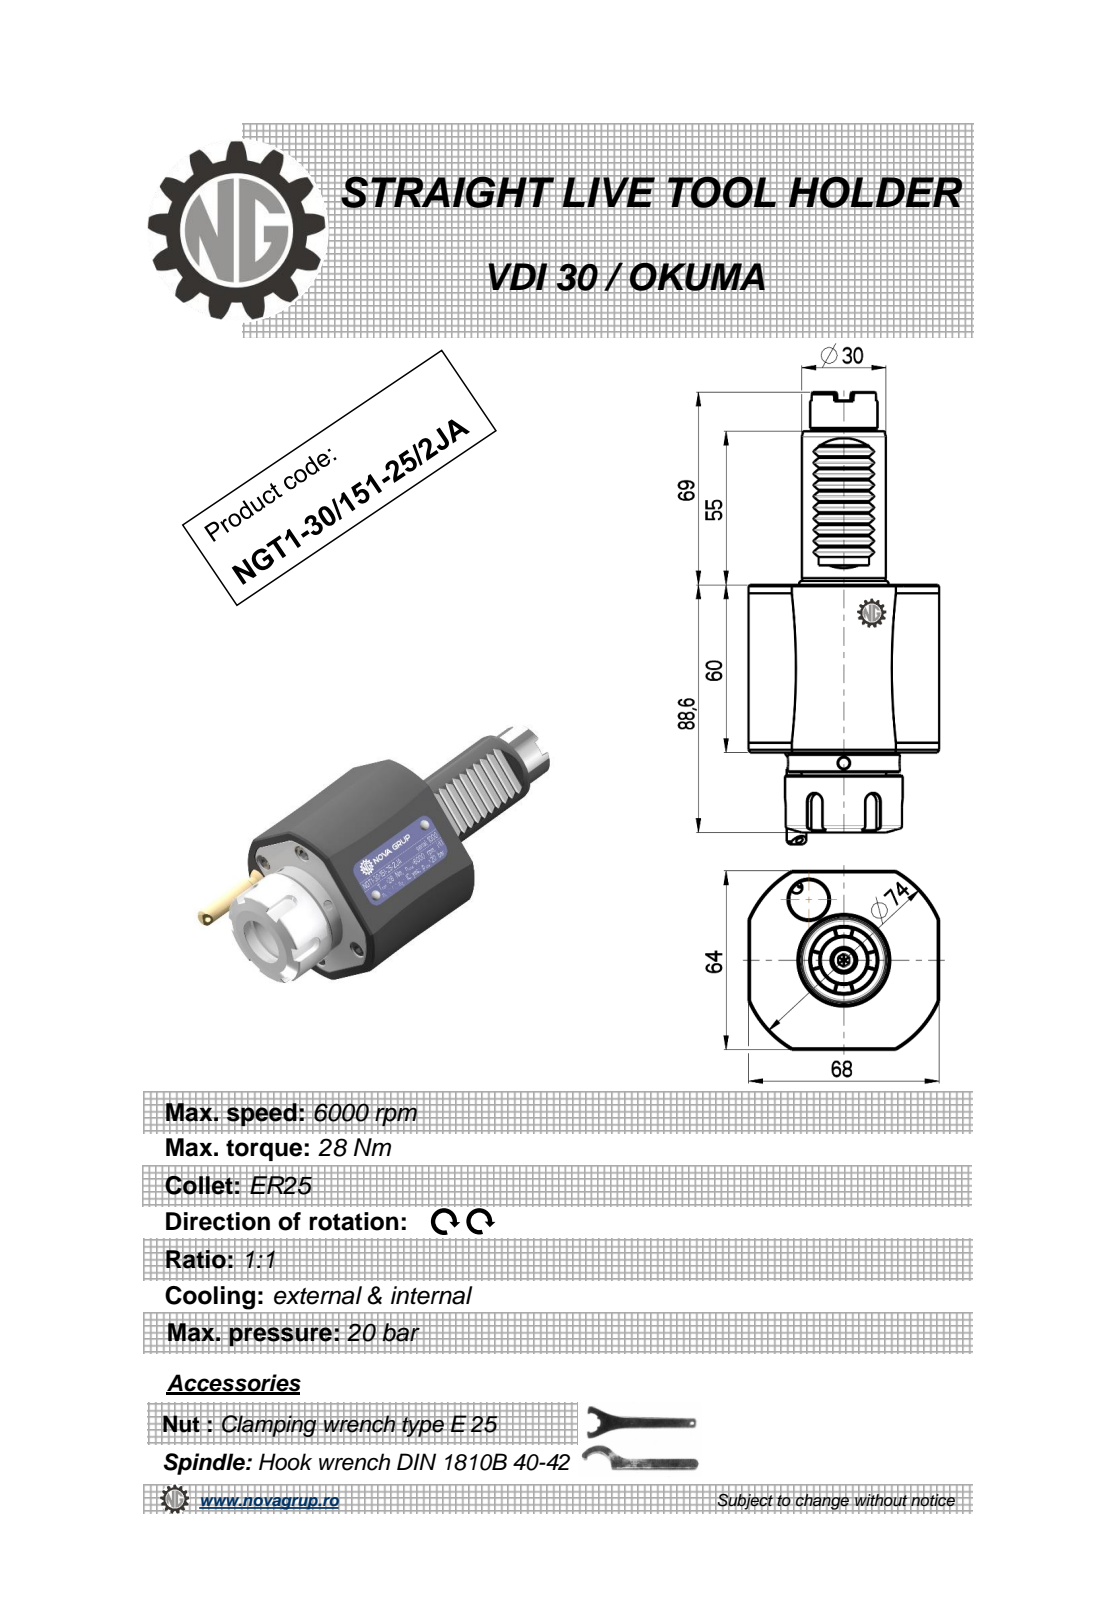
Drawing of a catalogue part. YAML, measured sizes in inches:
part_name: "NGT1_30_151_25_1JA"
step_written_by: "PRO/ENGINEER BY PARAMETRIC TECHNOLOGY CORPORATION, 2010280 (CONFIG_CONTROL_DESIGN)"
units: inches
bodies: {solids: 1, faces: 321, planar: 123, cylindrical: 66, other: 132}
overall_size: [6.371, 2.677, 2.583]
volume: 18.85
surface_area: 57.08
round_holes:
  - {diameter: 0.157, count: 2}
  - {diameter: 0.098, count: 1}
  - {diameter: 0.118, count: 1}
  - {diameter: 0.669, count: 1}
  - {diameter: 0.799, count: 1}
  - {diameter: 1.016, count: 1}
round_bosses_or_shafts:
  - {diameter: 1.654, count: 1}
  - {diameter: 1.575, count: 1}
  - {diameter: 1.299, count: 1}
  - {diameter: 1.181, count: 1}
  - {diameter: 0.945, count: 1}
  - {diameter: 0.65, count: 1}
  - {diameter: 0.354, count: 1}
  - {diameter: 0.276, count: 1}
partial_cylinders:
  - {radius: 0.012, count: 10}
  - {radius: 0.118, count: 5}
  - {radius: 0.547, count: 1}
  - {radius: 1.457, count: 1}
face_to_face_distances: [2.362, 2.52, 2.677, 0.111, 3.217, 0.854, 0.02, 2.681, 0.319, 0.535]
hole_center_spacings: [0.059, 1.171, 1.22]
